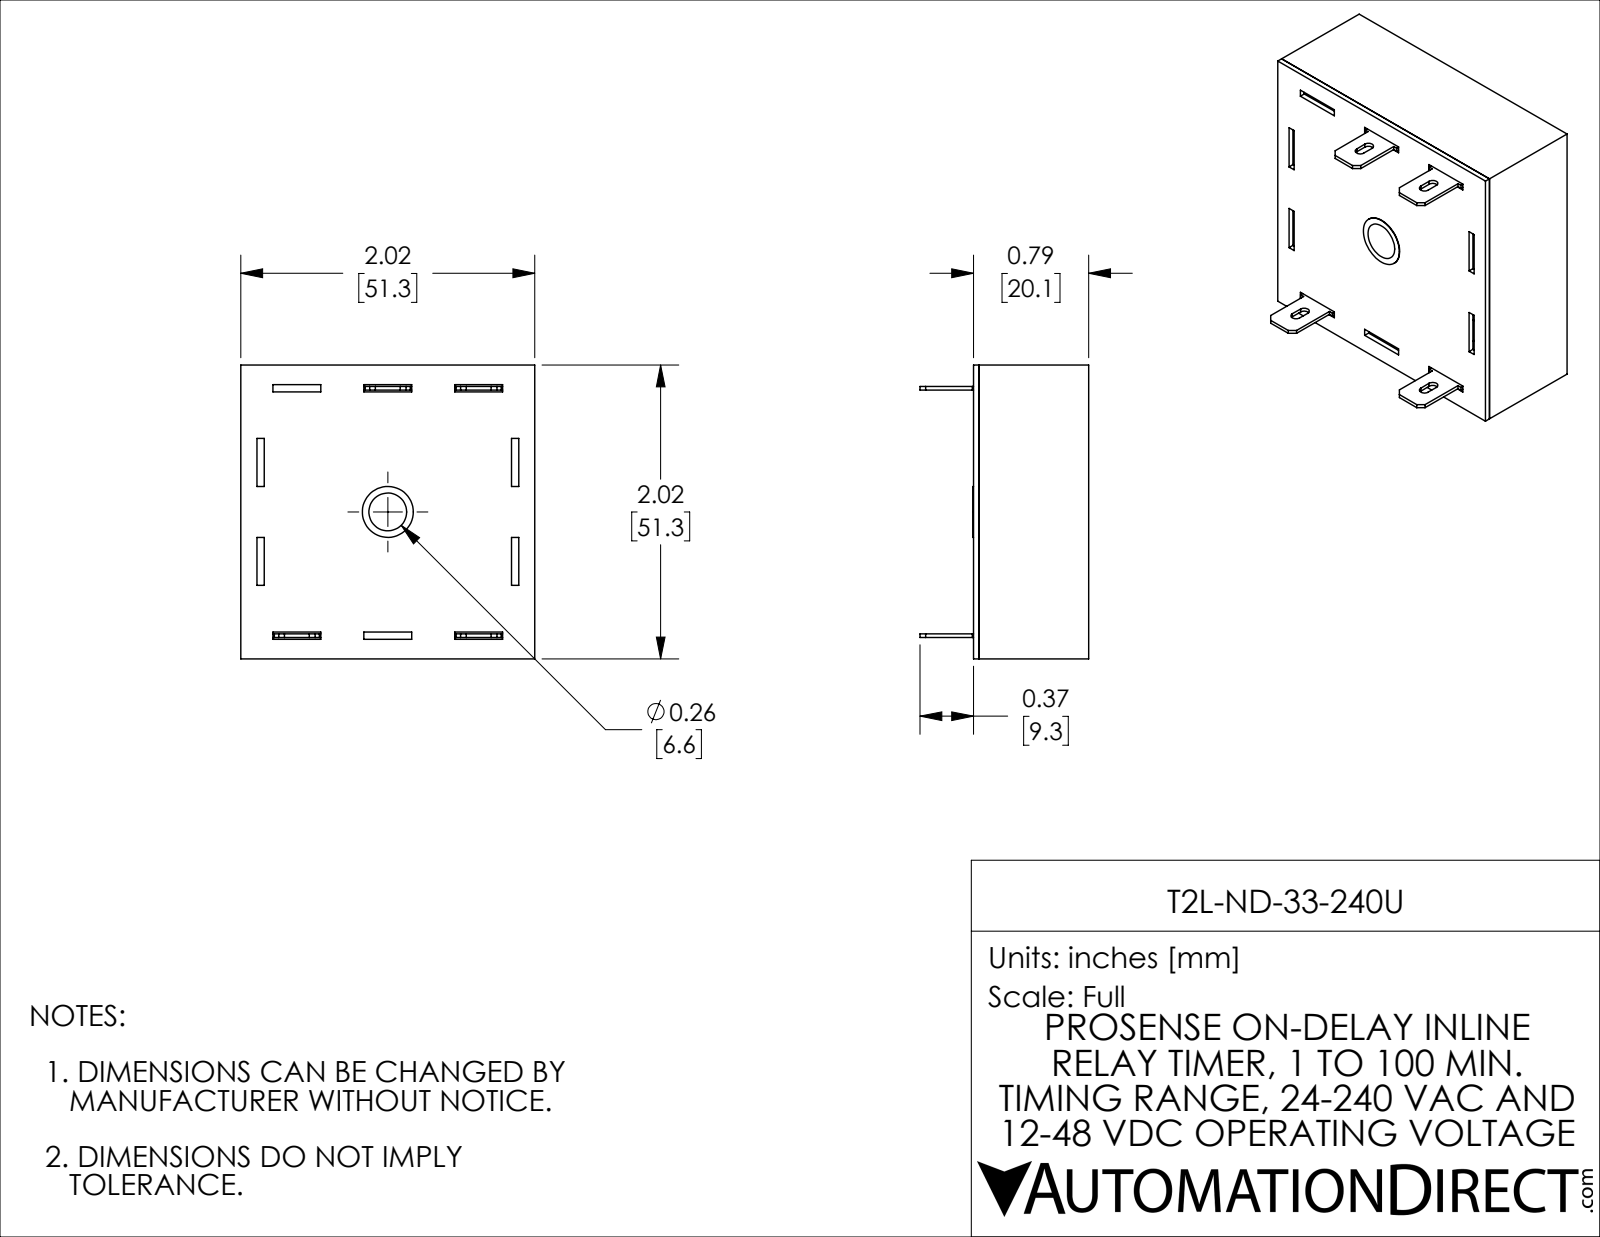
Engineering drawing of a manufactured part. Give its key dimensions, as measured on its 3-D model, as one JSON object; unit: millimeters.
{"part_name": "T2L-ND-33-240U", "step_written_by": "SolidWorks 2021 (CONFIG_CONTROL_DESIGN)", "units": "millimeters", "bodies": {"solids": 6, "faces": 160, "planar": 146, "cylindrical": 12, "other": 2}, "overall_size": [51.31, 51.31, 29.46], "volume_mm3": 10499, "surface_area_mm2": 20889, "round_holes": [[8.89, 1]], "partial_cylinders_radius": [[0.89, 6]], "face_to_face_distances": [1.14, 50.16, 19.15, 20.12, 0.97, 18.01, 18.98, 51.3, 49.02, 43.18]}
